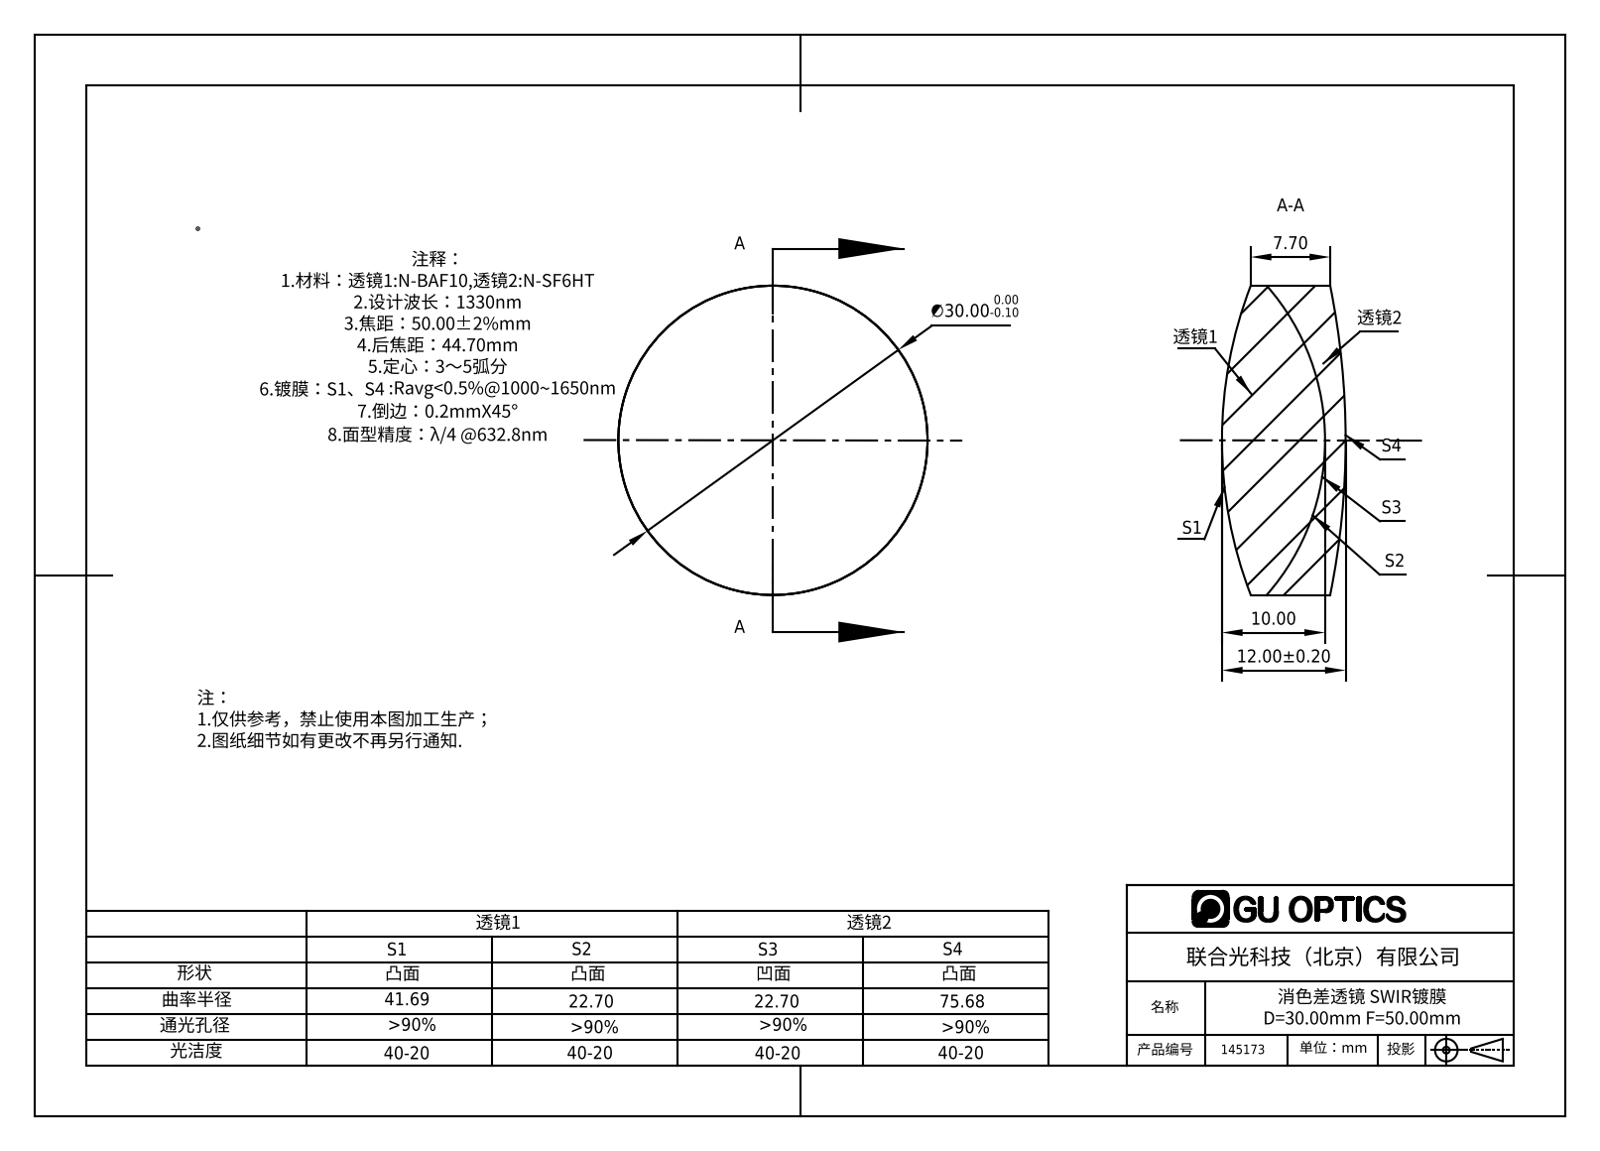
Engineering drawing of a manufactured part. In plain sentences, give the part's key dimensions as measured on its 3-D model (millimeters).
The part is named "145173". Its 3-D file was written by "SolidWorks 2016 (AUTOMOTIVE_DESIGN)". It is 2 solids with 12 faces: 0 planar, 4 cylindrical and 8 other. Overall it measures 30 by 30 by 12 millimeters. Its volume is 6 978 cubic millimeters and its surface area 3 787 square millimeters. Round bosses or shafts: 1 of diameter 30.
